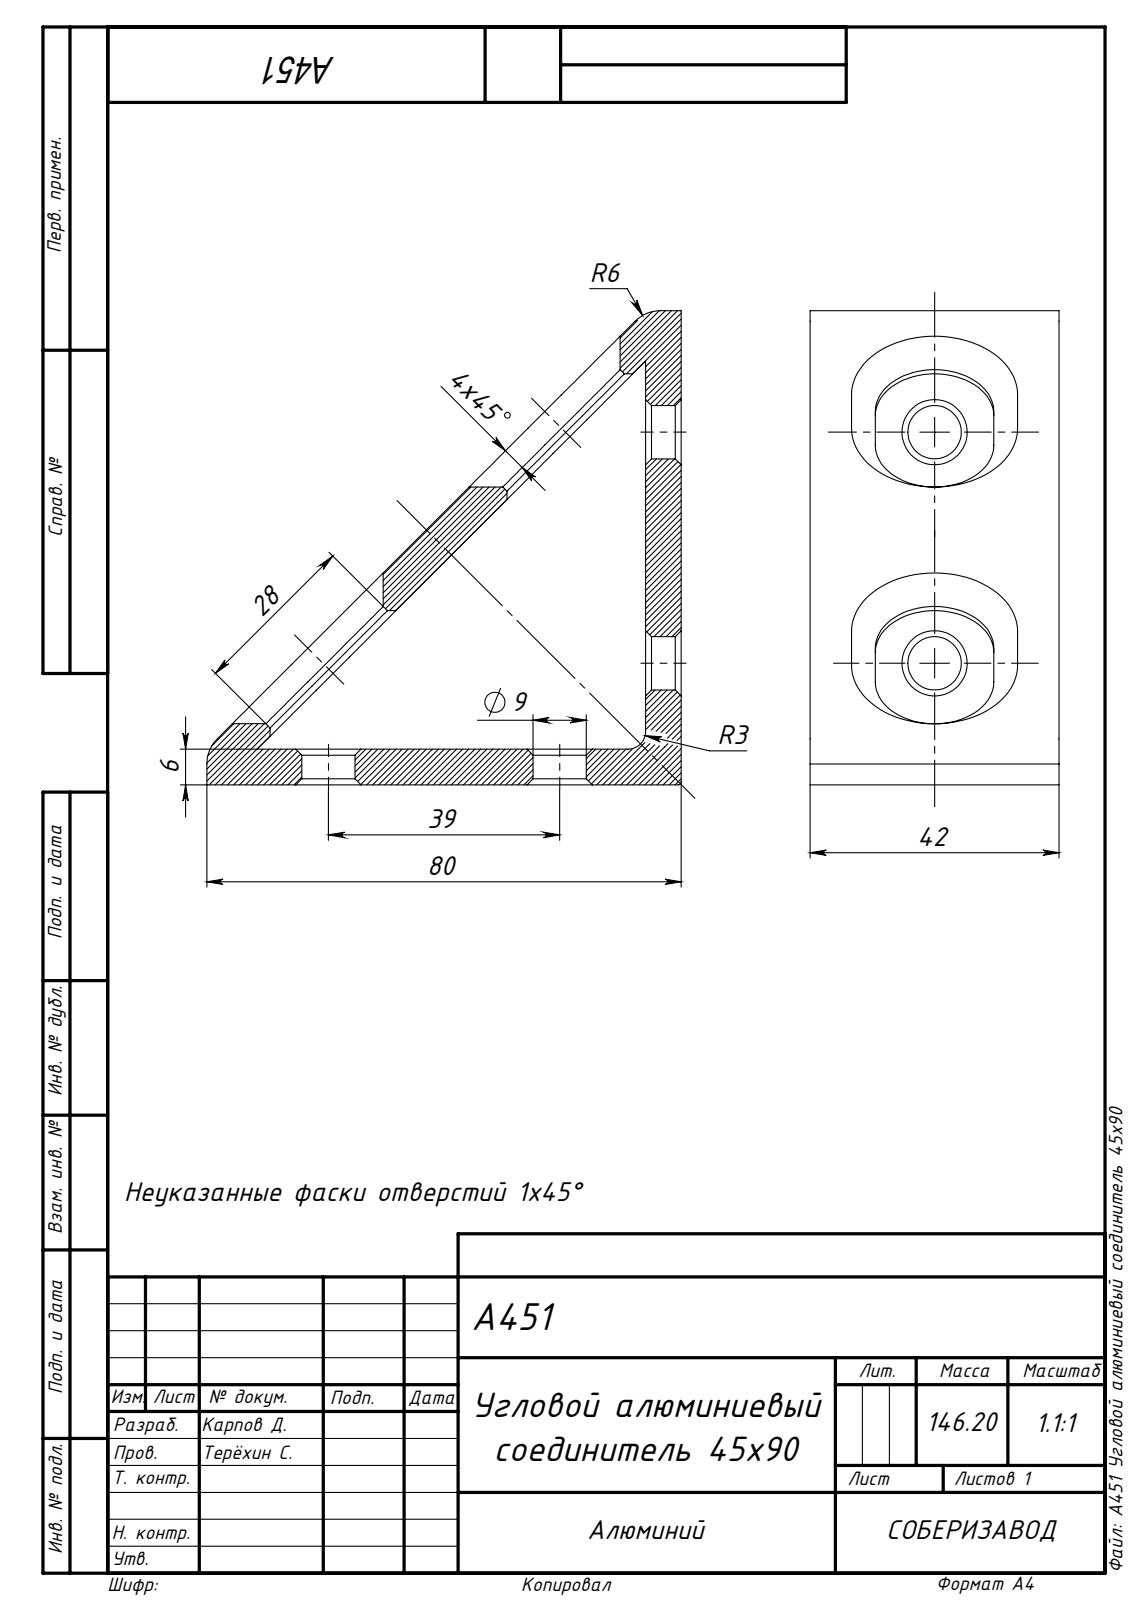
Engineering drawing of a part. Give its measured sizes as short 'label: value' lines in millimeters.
name: A451 Угловой алюминиевый соединитель 45х90
written by: SolidWorks 2021 (AUTOMOTIVE_DESIGN)
unit: mm
bodies: 1 solid, 68 faces (22 planar, 18 cylindrical, 28 other)
size: 80 × 80 × 42
volume: 54 868 mm³; area: 22 641 mm²
holes: 4× ⌀9
rounds: 4× R10, 2× R6, 1× R0.5, 1× R3
face distances: 6, 42, 80, 74, 11, 31, 13.43, 13.44, 20
hole spacings: 39
